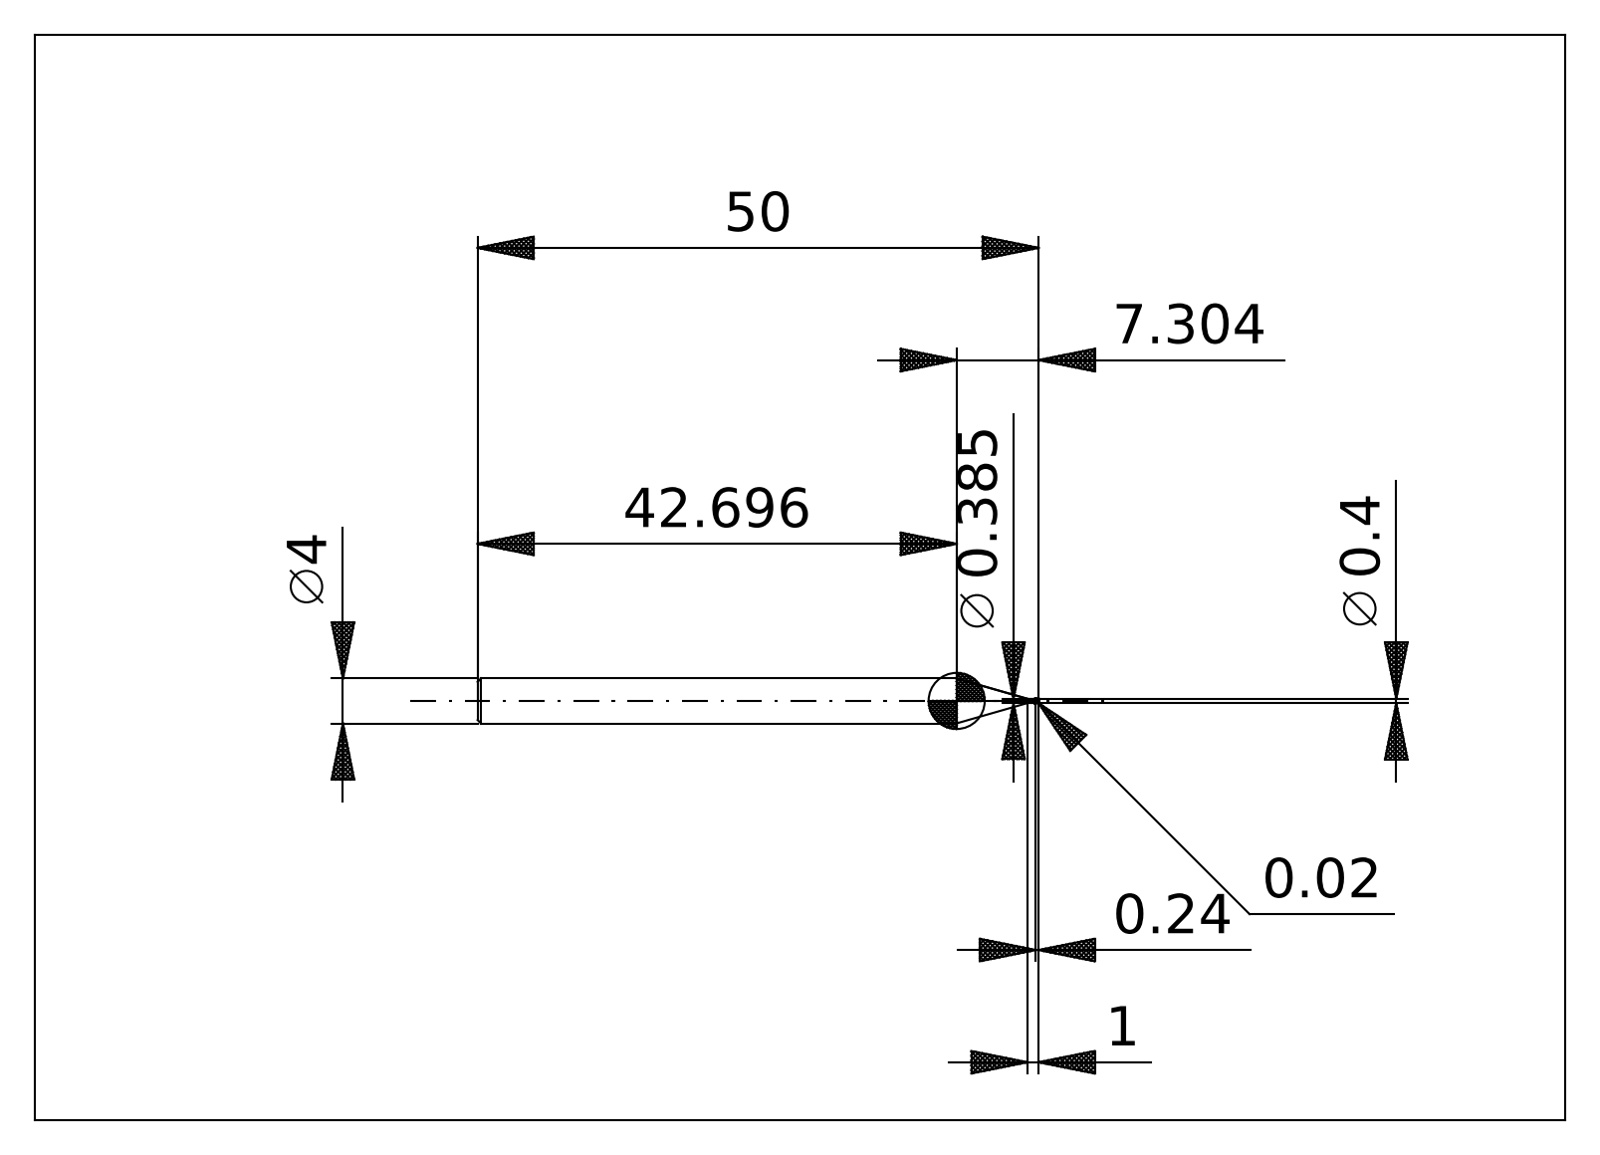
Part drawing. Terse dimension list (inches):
written by: ACIS (automotive_design)
unit: in
bodies: 2 solids, 26 faces (6 planar, 8 cylindrical, 12 other)
size: 1.969 × 0.157 × 0.157
volume: 0.034 in³; area: 0.921 in²
bosses: 1× ⌀0.157, 1× ⌀0.015
face distances: 1.969, 1.966, 1.959, 0.287, 0.285, 0.278, 1.681
